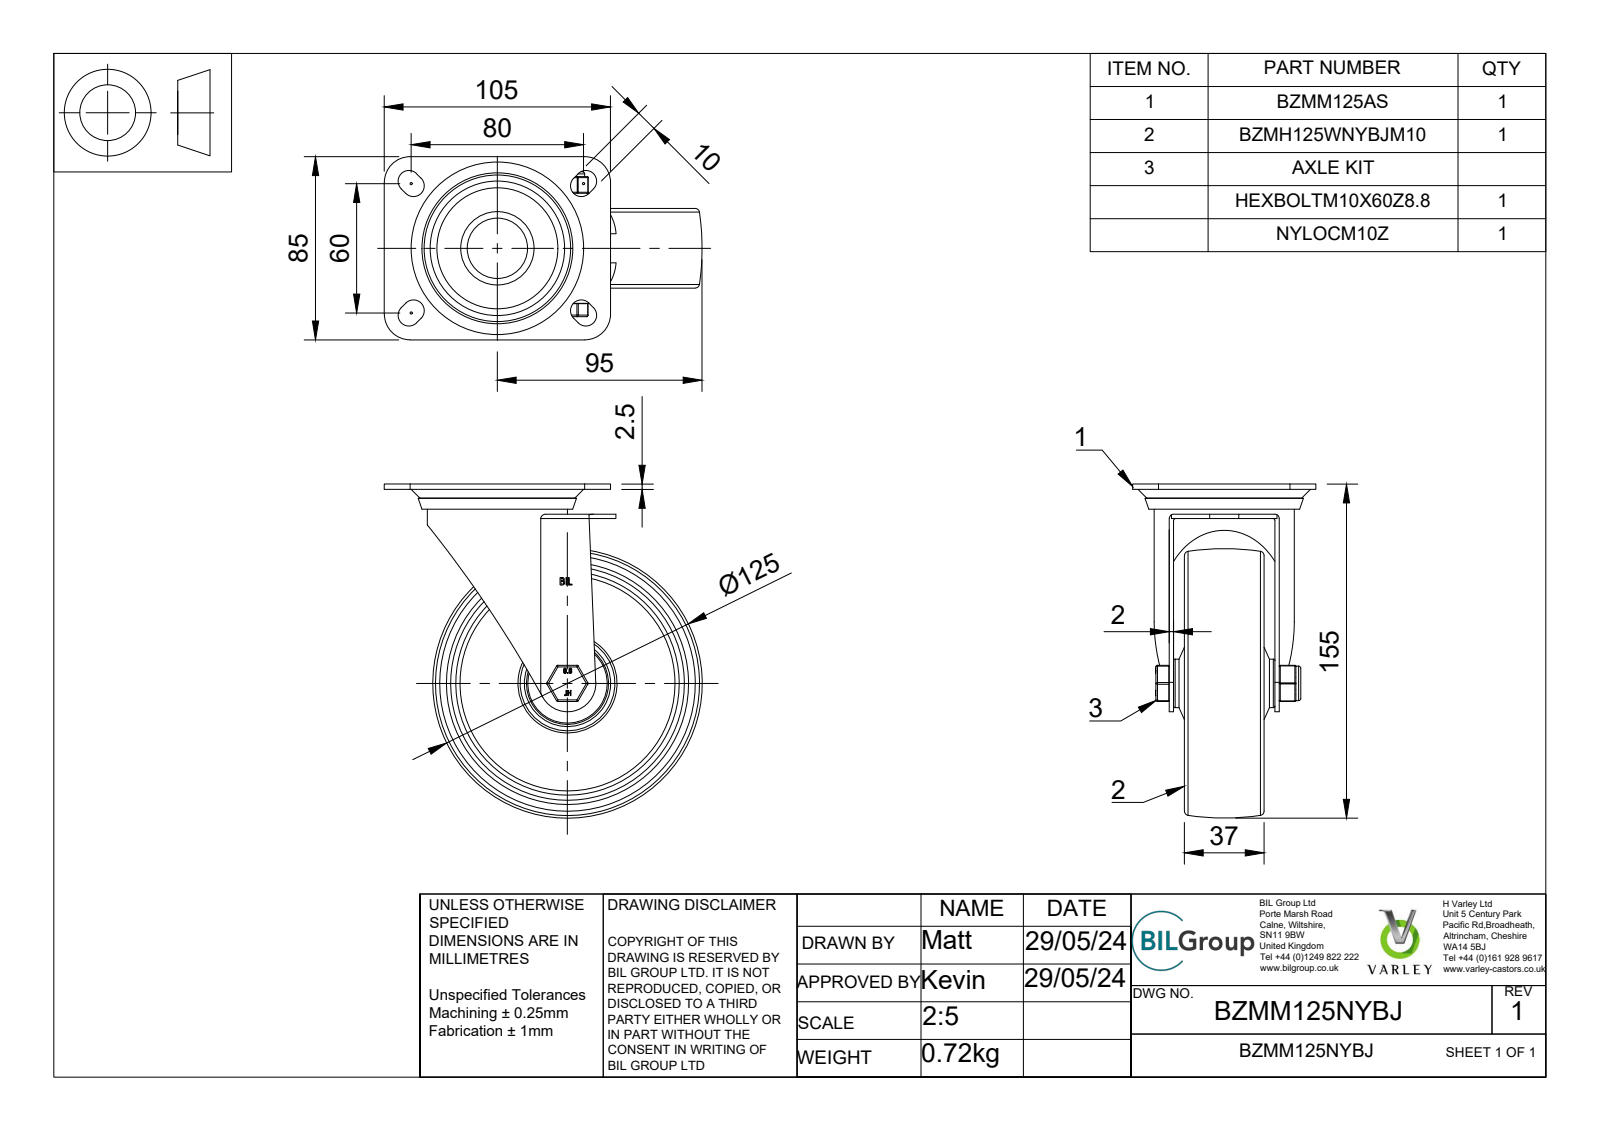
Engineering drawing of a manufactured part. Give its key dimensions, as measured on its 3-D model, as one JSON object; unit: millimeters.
{"part_name": "BZMM125NYBJ v3; BZMM125AS - 2 - 47 v1; ZINC PLATED, PRESSED STEEL TOP PLATE; ZINC PLATED, PRESSED STEEL FORKS (+8 more)", "step_written_by": "Autodesk Translation Framework v13.14.0.145 (AUTOMOTIVE_DESIGN)", "units": "millimeters", "bodies": {"solids": 22, "faces": 729, "planar": 275, "cylindrical": 173, "other": 281}, "overall_size": [155, 147.5, 85], "volume_mm3": 280218, "surface_area_mm2": 129932, "round_holes": [[10, 1], [10.2, 1], [10.3, 1], [12, 1], [15, 1], [20, 1], [22.5, 1], [25, 1], [28, 1], [30, 1], [31, 1], [32, 1]], "round_bosses_or_shafts": [[65, 1], [49, 1], [44, 1], [38, 1], [34, 1], [30.5, 1], [28, 1], [23, 1]], "partial_cylinders_radius": [[0.5, 18], [0.75, 12], [5, 8], [12, 5], [1, 4], [2, 2], [20.69, 2], [13.14, 1]], "face_to_face_distances": [7, 2, 5, 22, 20, 29, 2.5, 27, 49, 9]}
